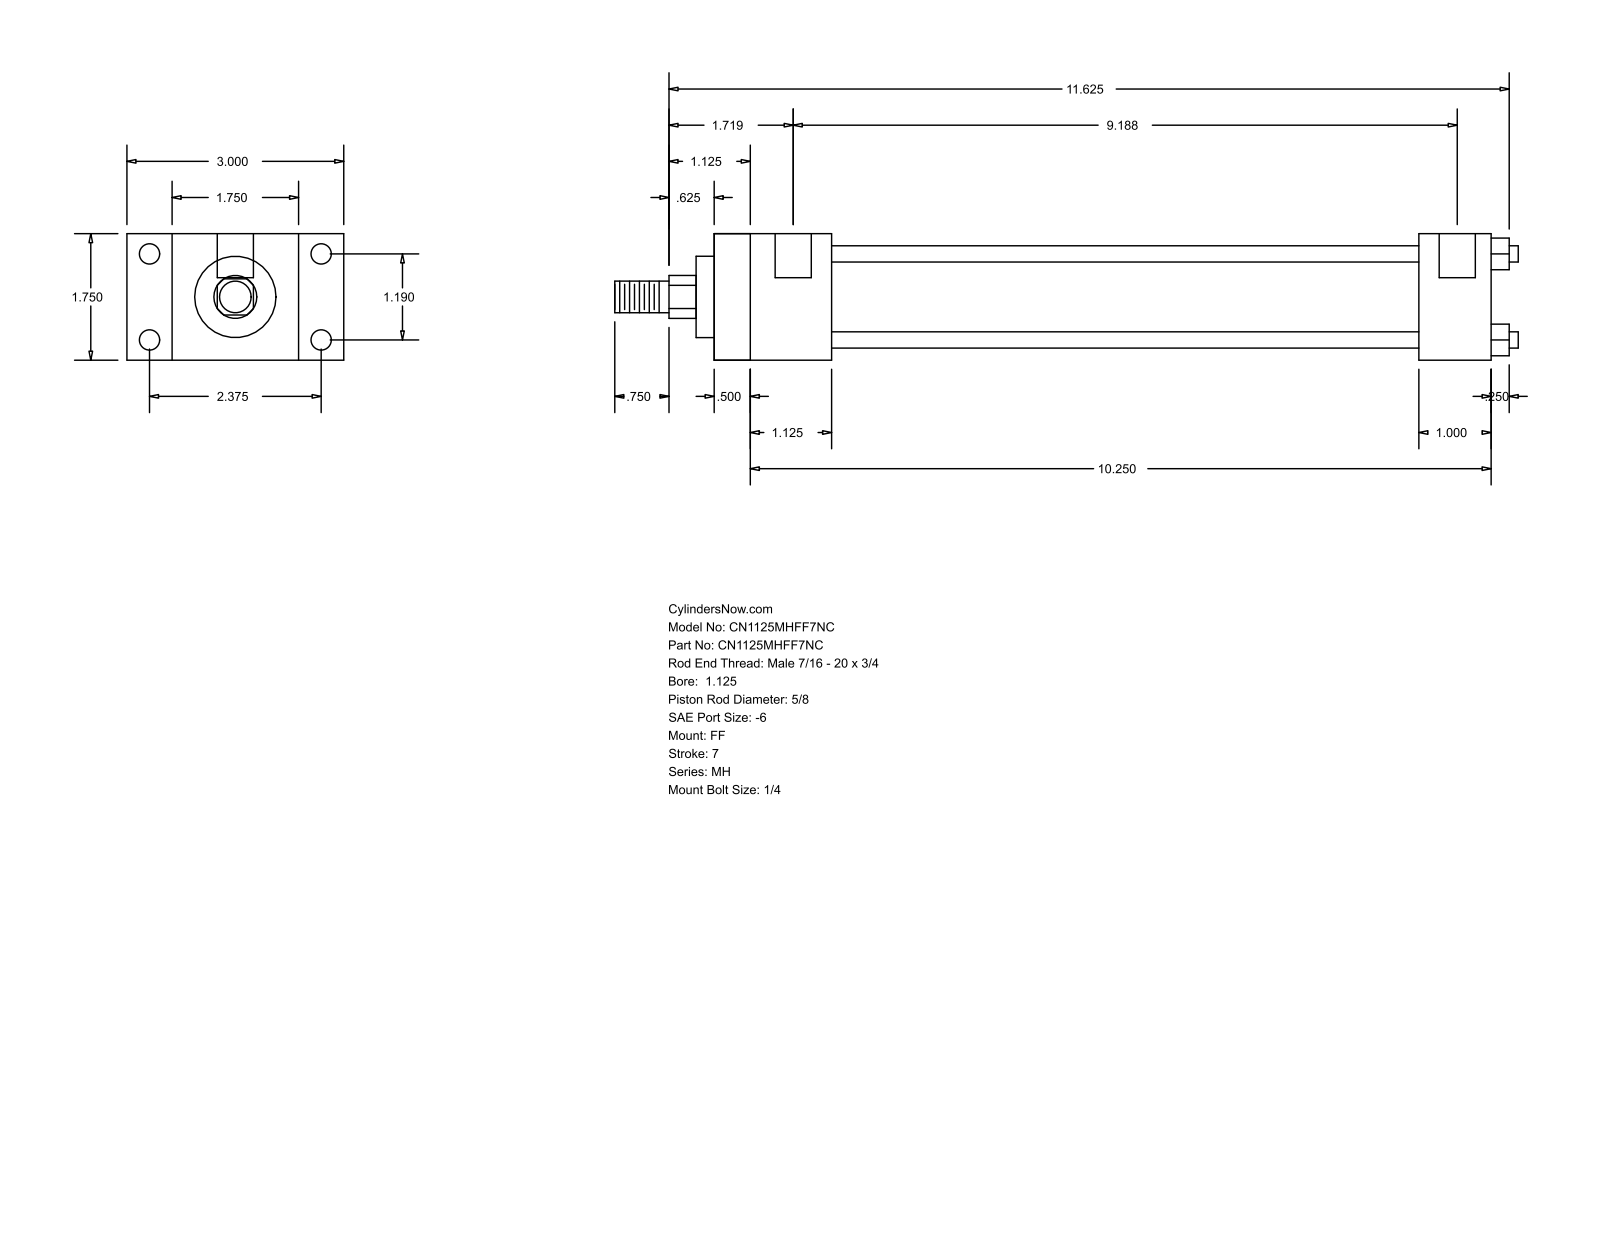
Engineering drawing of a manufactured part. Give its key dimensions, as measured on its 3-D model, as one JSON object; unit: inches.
{"part_name": "MH_FF__0112_0.625", "step_written_by": "GSSL Pune (CONFIG_CONTROL_DESIGN)", "units": "inches", "bodies": {"solids": 0, "faces": 92, "planar": 64, "cylindrical": 28, "other": 0}, "overall_size": [12.5, 3, 1.75], "round_holes": [[0.219, 4], [0.281, 4], [0.5, 2]], "round_bosses_or_shafts": [[0.225, 4], [1.375, 1], [1.125, 1], [0.625, 1], [0.437, 1]], "partial_cylinders_radius": [[0.297, 1]], "face_to_face_distances": [1.75, 10.75, 0.625, 0.5, 10.25, 1.125, 2.375, 1.625, 9.75, 9.25], "hole_center_spacings": [1.19, 2.375, 2.656, 9.063, 0.125, 9.187]}
